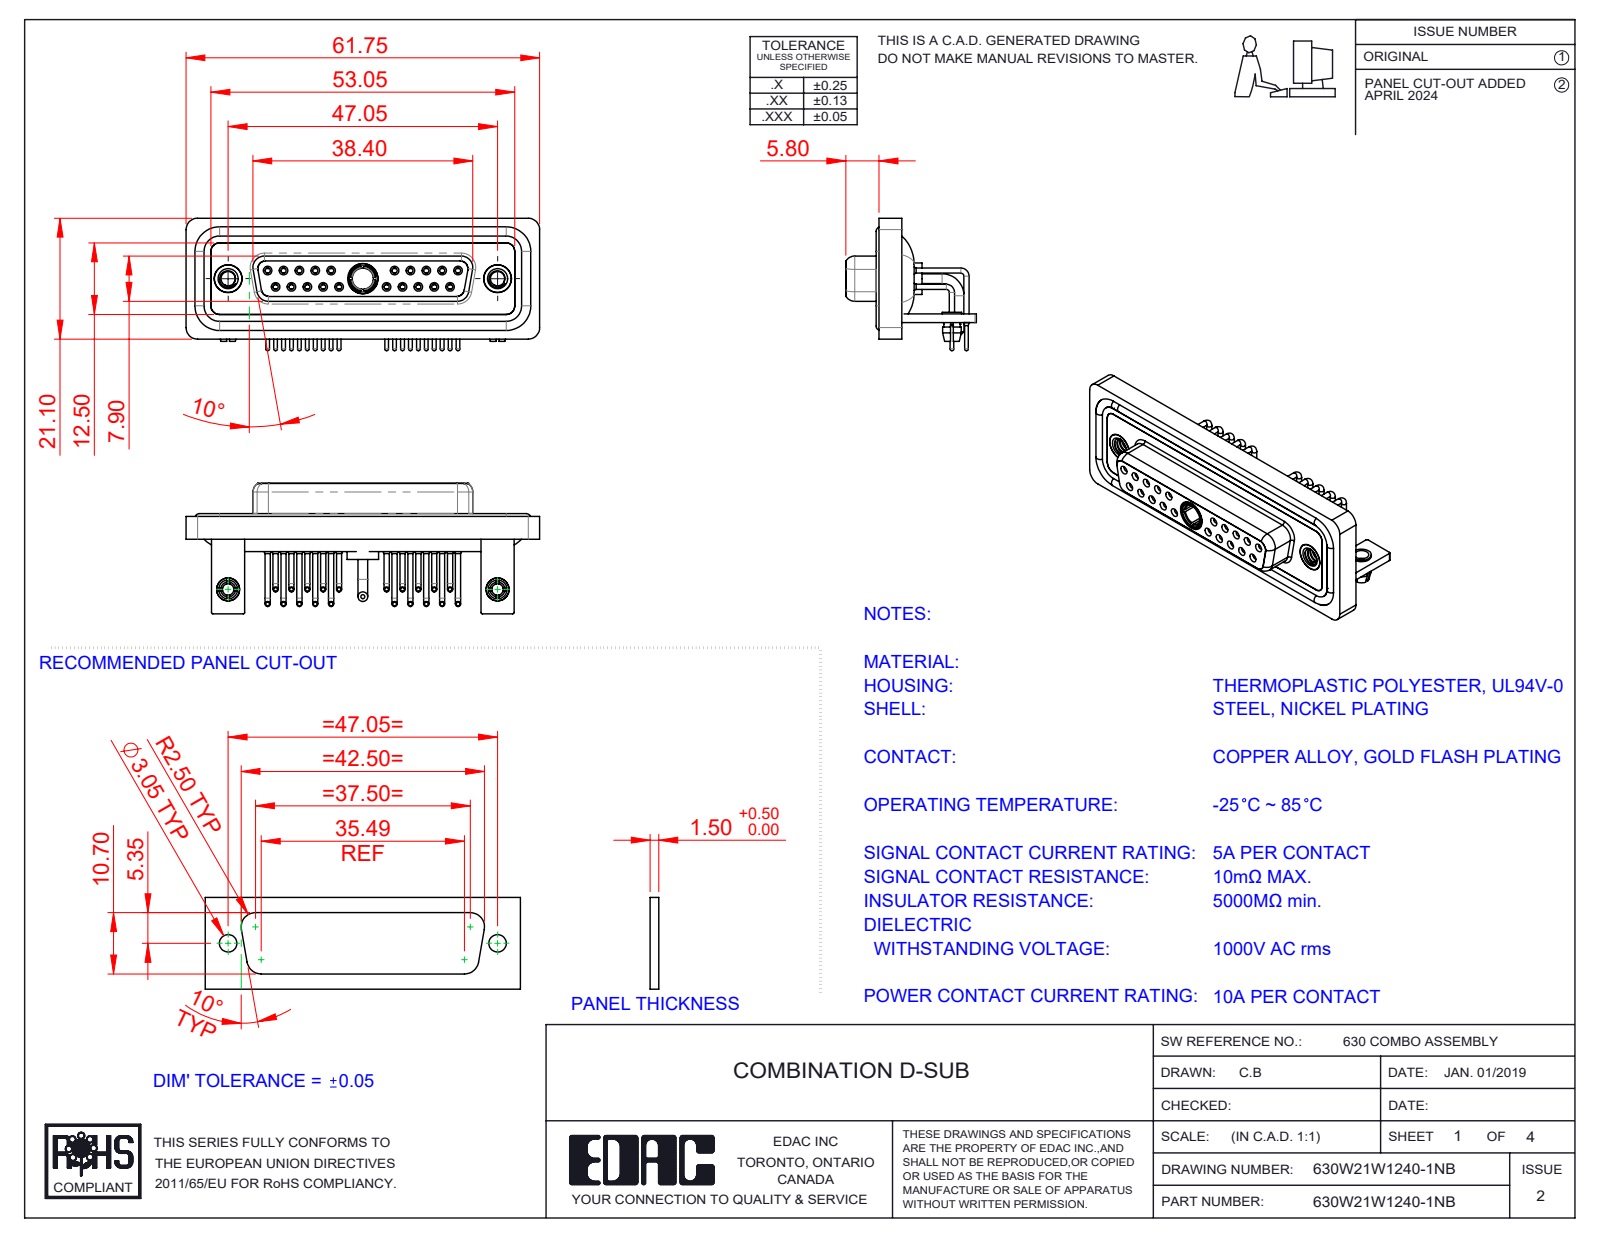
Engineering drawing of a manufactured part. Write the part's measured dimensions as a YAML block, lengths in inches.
part_name: "630W21W1140-1NB; 630Combo Shell Rear_25 Contacts; 630Combo Board Lock_50 Contacts; 630Combo Waterproof Housing_25 Contacts (+7 more)"
step_written_by: "SolidWorks 2023 (CONFIG_CONTROL_DESIGN)"
units: inches
bodies: {solids: 33, faces: 1658, planar: 502, cylindrical: 727, other: 429}
overall_size: [2.431, 0.91, 0.898]
volume: 0.54
surface_area: 24.3
round_holes:
  - {diameter: 0.079, count: 22}
  - {diameter: 0.035, count: 20}
  - {diameter: 0.043, count: 20}
  - {diameter: 0.059, count: 20}
  - {diameter: 0.063, count: 10}
  - {diameter: 0.067, count: 10}
  - {diameter: 0.098, count: 4}
  - {diameter: 0.191, count: 3}
  - {diameter: 0.126, count: 2}
  - {diameter: 0.157, count: 2}
  - {diameter: 0.159, count: 2}
  - {diameter: 0.197, count: 2}
round_bosses_or_shafts:
  - {diameter: 0.035, count: 20}
  - {diameter: 0.026, count: 20}
  - {diameter: 0.063, count: 14}
  - {diameter: 0.195, count: 2}
  - {diameter: 0.189, count: 2}
  - {diameter: 0.157, count: 2}
  - {diameter: 0.134, count: 2}
  - {diameter: 0.13, count: 2}
partial_cylinders:
  - {radius: 0.079, count: 19}
  - {radius: 0.059, count: 18}
  - {radius: 0.01, count: 16}
  - {radius: 0.053, count: 8}
  - {radius: 0.063, count: 8}
  - {radius: 0.02, count: 5}
  - {radius: 0.024, count: 4}
  - {radius: 0.026, count: 4}
face_to_face_distances: [0.016, 0.071, 0.114, 0.146, 0.059, 0.161, 0.043, 0.055, 0.063, 0.098]
hole_center_spacings: [0.124, 0.109, 0.218, 0.327, 0.198, 0.763, 0.826, 0.872]
